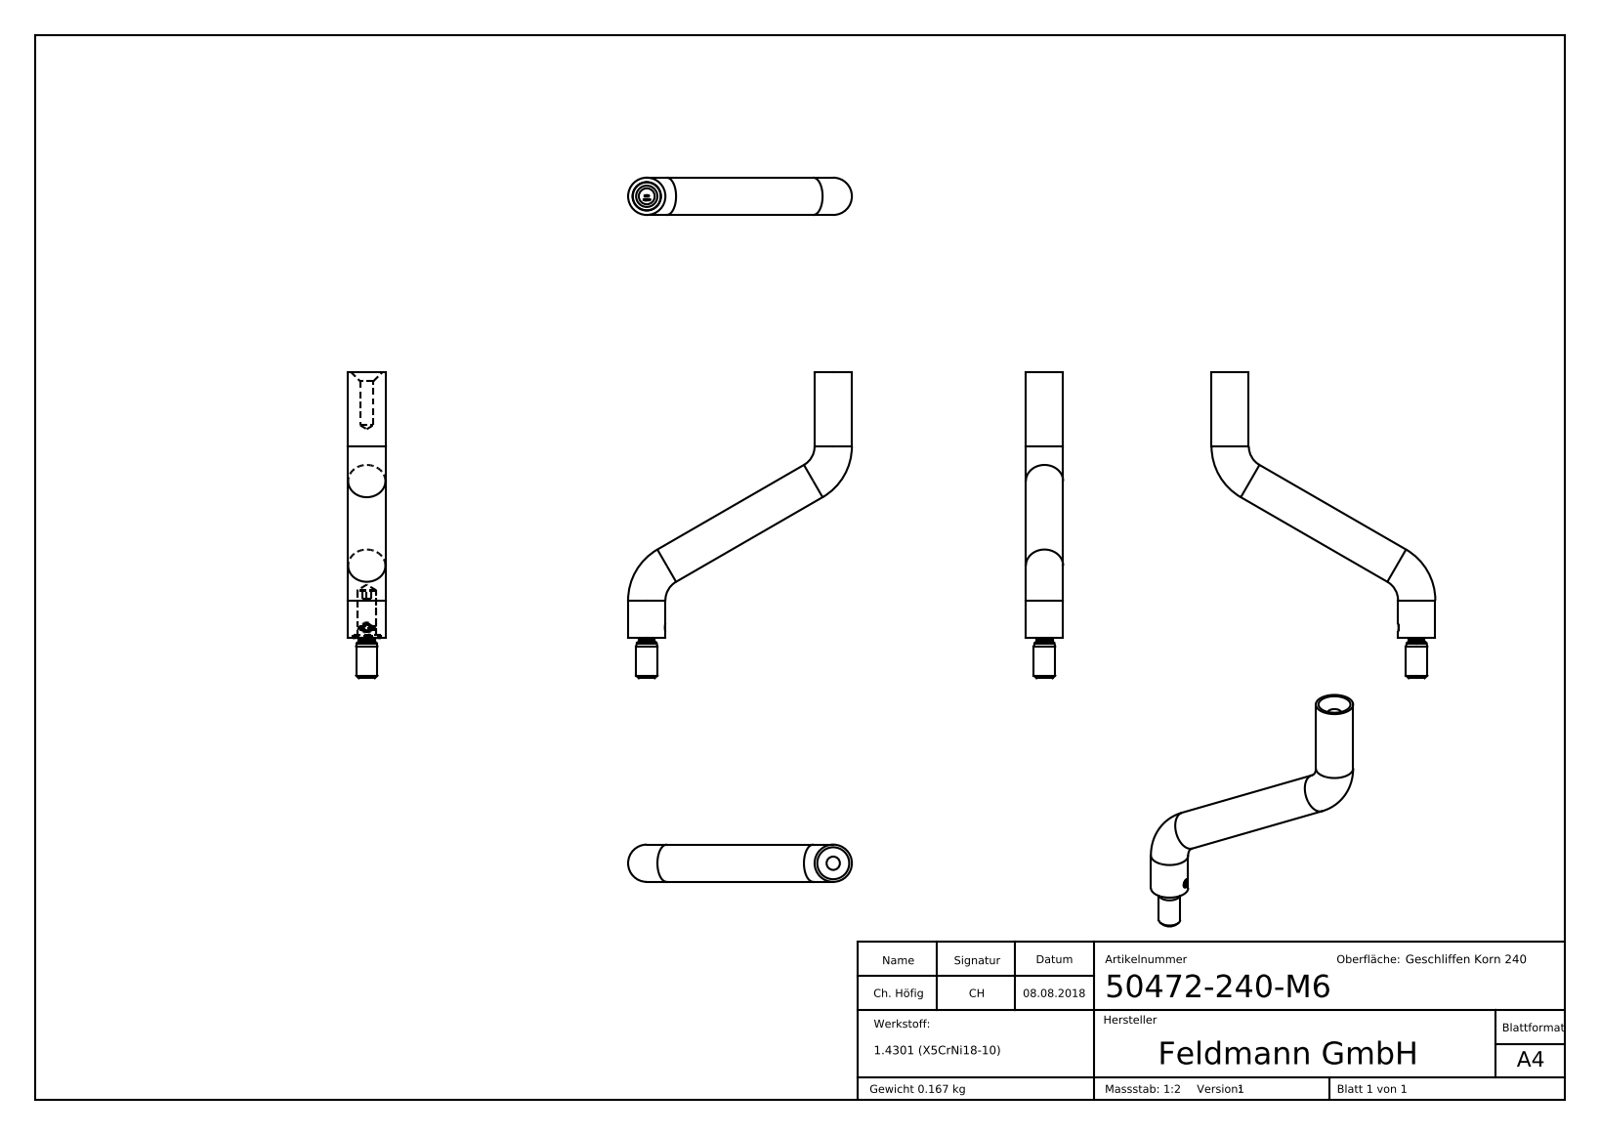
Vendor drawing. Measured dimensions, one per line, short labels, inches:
name: 50472-240 Teil2_50472-240-M6 Teil2; 50472-240-M6; DIN 914_-_M04 x 04_DIN 914 M4 x 4; 50472-240 Teil1_50472-240-M6 Teil1
written by: SolidWorks 2015 (CONFIG_CONTROL_DESIGN)
unit: in
bodies: 3 solids, 341 faces (182 planar, 26 cylindrical, 133 other)
size: 4.528 × 3.307 × 0.551
volume: 1.292 in³; area: 12.64 in²
holes: 1× ⌀0.13, 1× ⌀0.197, 1× ⌀0.28, 1× ⌀0.421
bosses: 3× ⌀0.551, 1× ⌀0.413, 1× ⌀0.315, 1× ⌀0.276, 1× ⌀0.236, 1× ⌀0.157
face distances: 0.047, 0.039, 3.937, 3.898, 3.89, 0.591, 0.63, 0.638, 4.528, 1.299
hole spacings: 2.756
